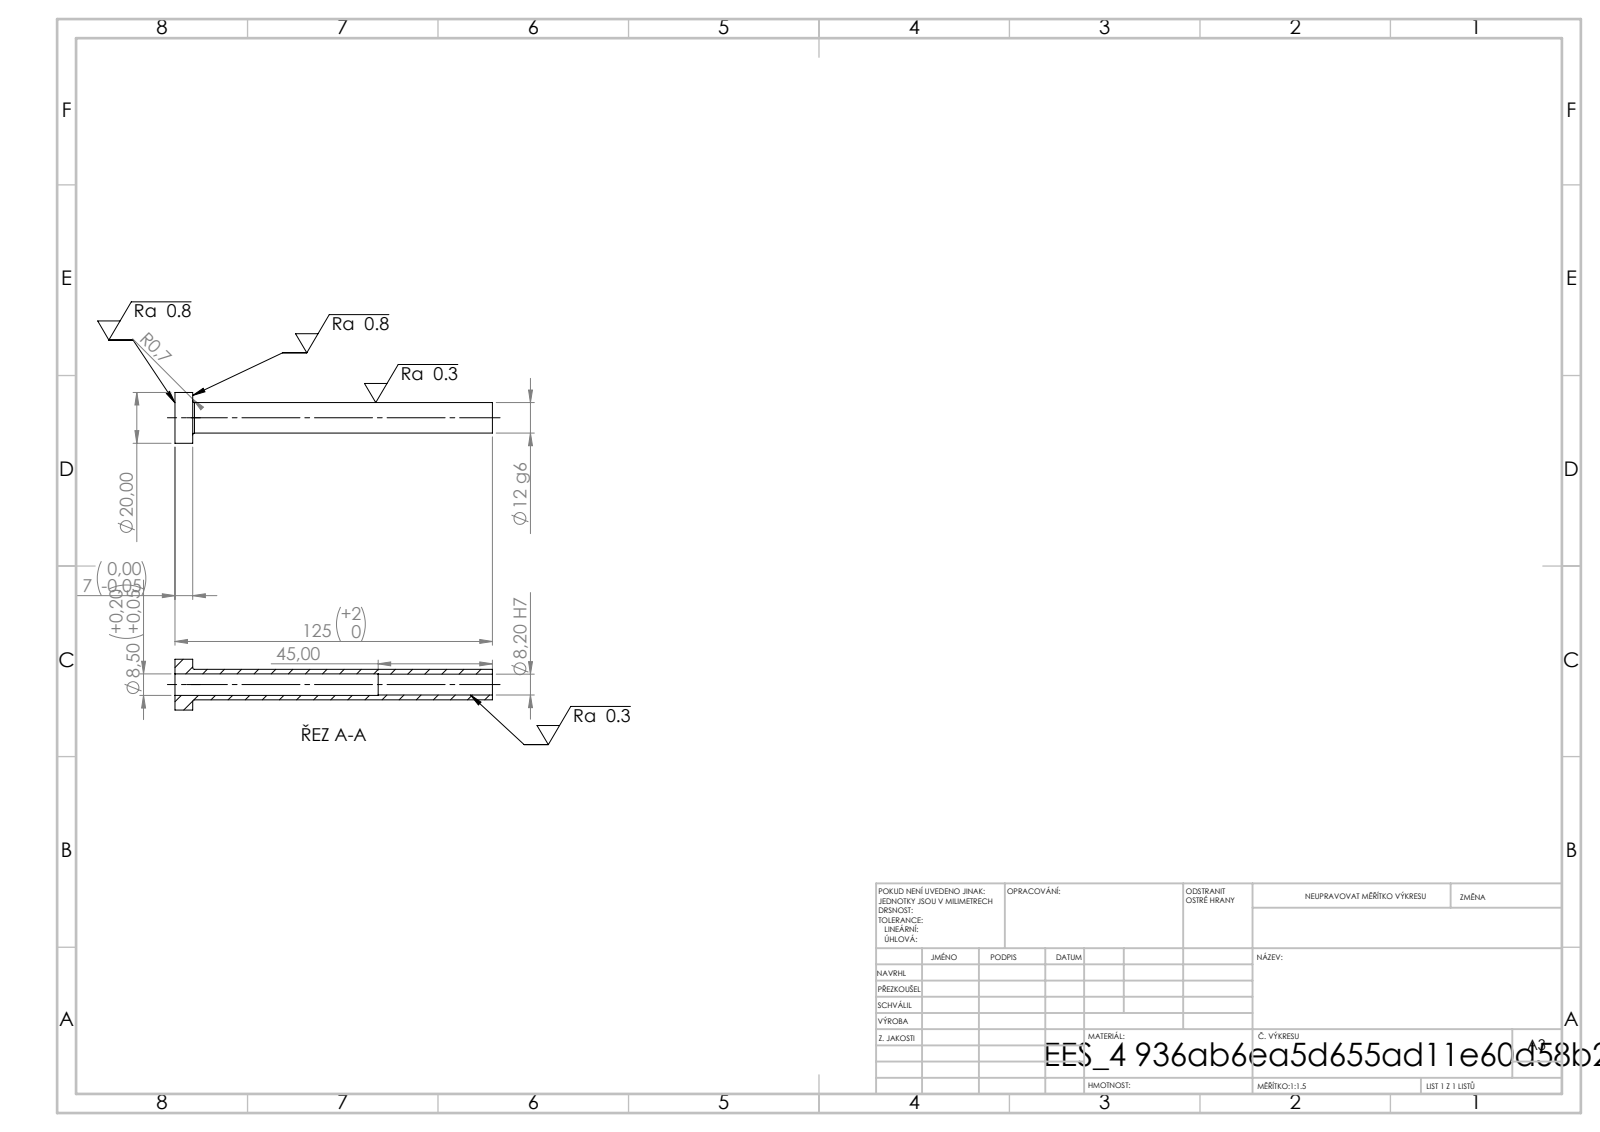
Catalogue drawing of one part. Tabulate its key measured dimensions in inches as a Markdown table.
| quantity | value |
| --- | --- |
| STEP written by | SolidWorks 2019 (CONFIG_CONTROL_DESIGN) |
| units | inches |
| bodies | 1 solid, 14 faces (4 planar, 8 cylindrical, 2 other) |
| overall size | 4.921 × 0.787 × 0.787 |
| volume | 0.527 in³ |
| surface area | 13.48 in² |
| round holes (diameter × count) | 0.323 × 1, 0.335 × 1 |
| round bosses / shafts (diameter × count) | 0.787 × 1, 0.472 × 1 |
| main face-to-face distances | 0.276, 4.921, 4.646, 3.15, 2.874, 1.772 |
